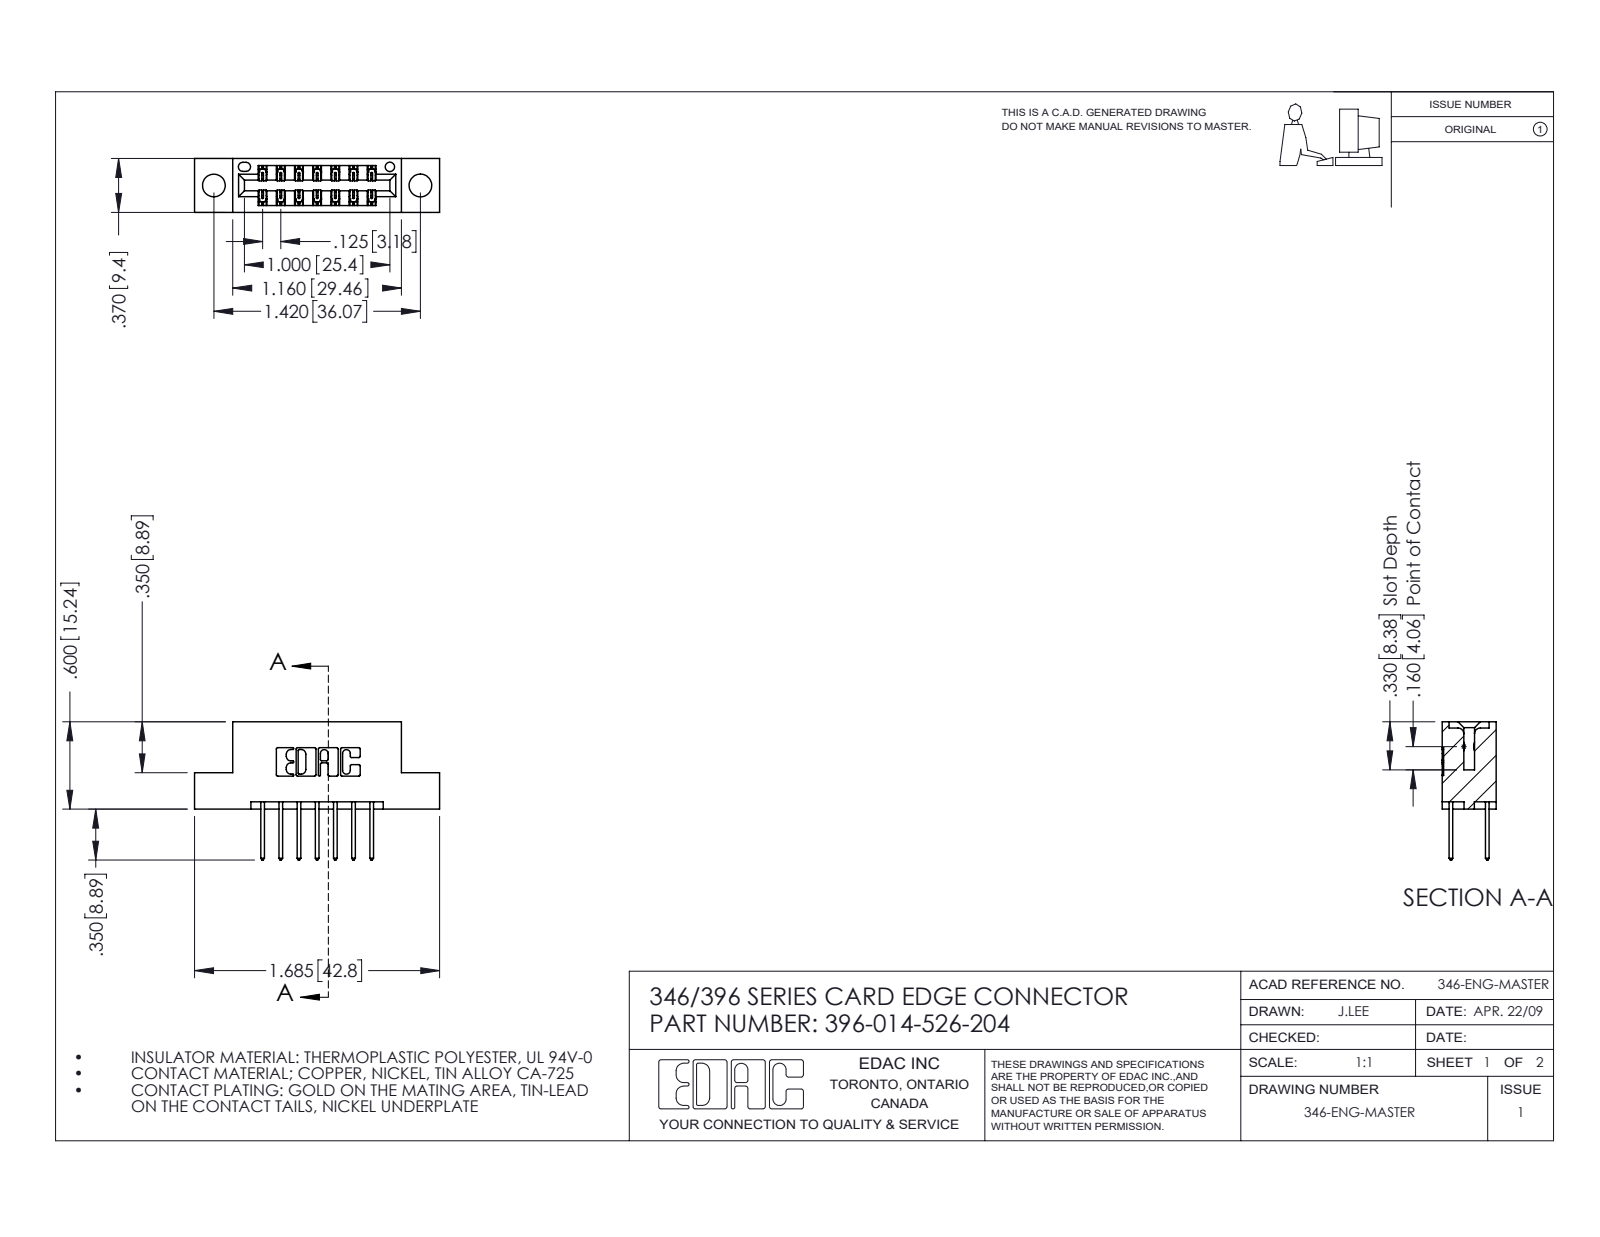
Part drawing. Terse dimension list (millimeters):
name: 345-292-001_345-293-126; 396-014-526-204; 346 Part_Flush Mounting Lugs - 0.156 Dia-TH
written by: SolidWorks 2016 (CONFIG_CONTROL_DESIGN)
unit: mm
bodies: 15 solids, 850 faces (566 planar, 284 cylindrical, 0 other)
size: 42.8 × 24.1 × 9.4
volume: 3 830 mm³; area: 4 640 mm²
holes: 2× ⌀4, 1× ⌀1.6
rounds: 22× R0.3, 21× R0.2, 14× R0.3, 6× R0.2, 6× R0.8, 3× R0.7, 2× R0.4, 2× R0.6
face distances: 6.4, 1.2, 8.2, 9.4, 1.8, 7.6, 0.6, 7, 3.8, 5.6
hole spacings: 6.2, 30.9, 36.1
